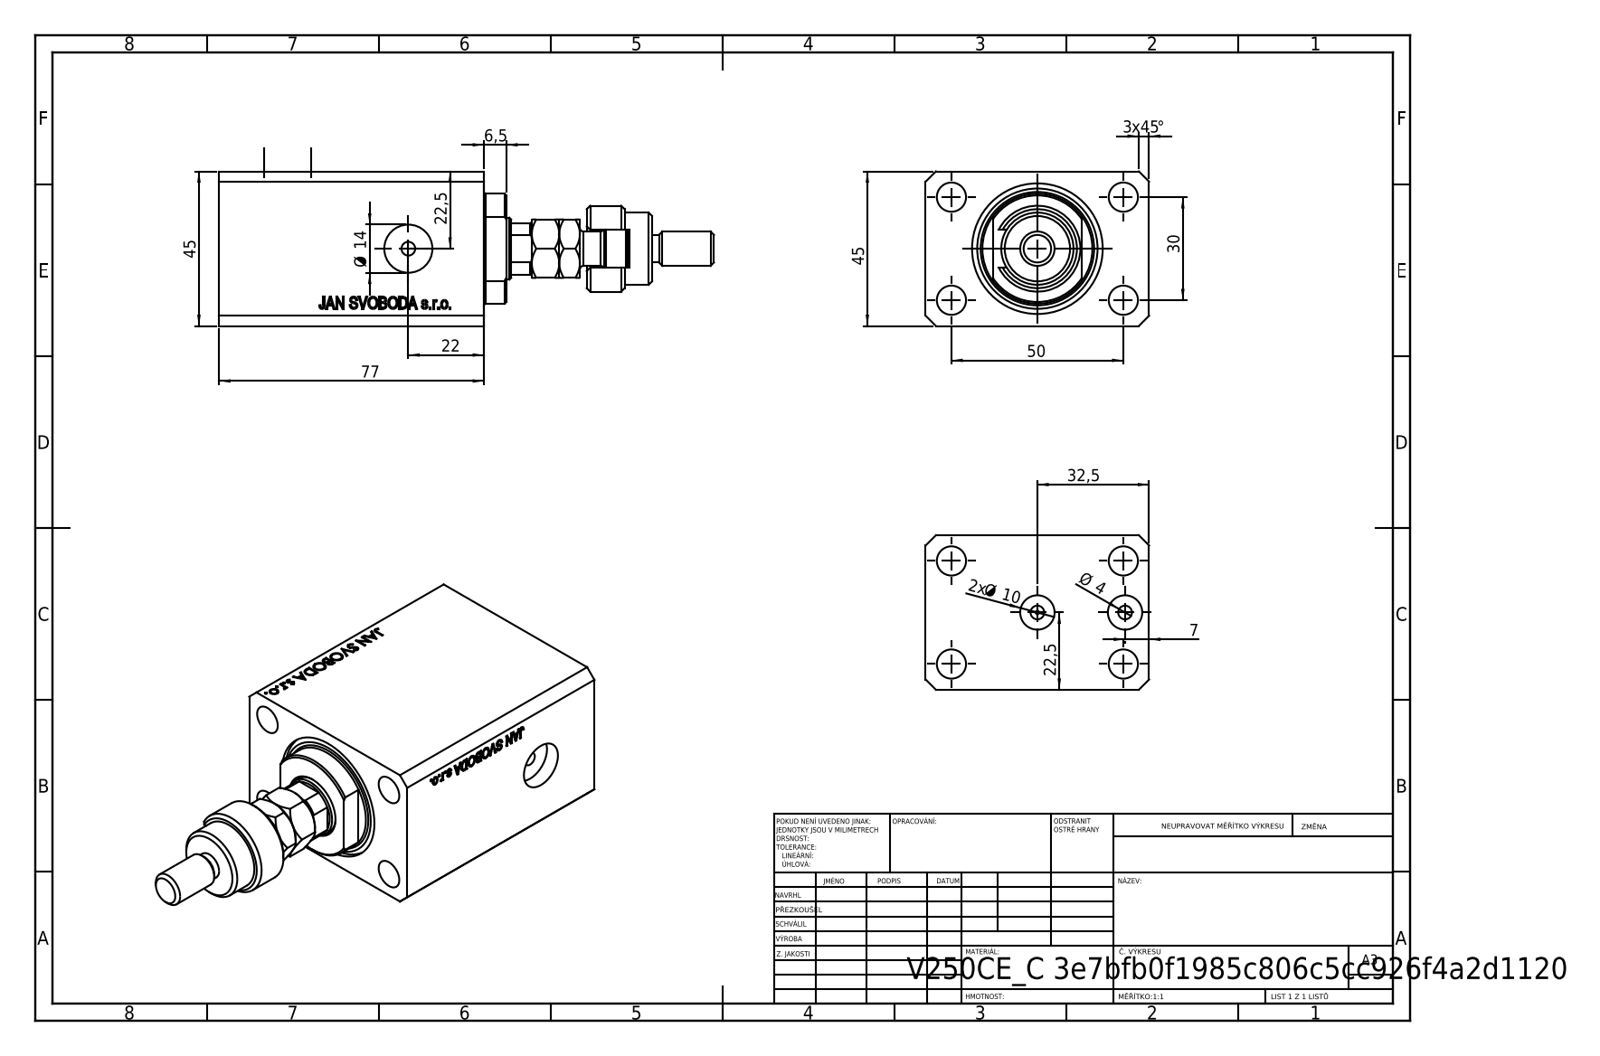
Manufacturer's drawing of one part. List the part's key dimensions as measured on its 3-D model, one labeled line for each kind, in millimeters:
Part name (STEP PRODUCT): V250CE_VC_C; MFA; V250CE_C_Body; FEMALE_PART_FOR_DFA (+1 more)
STEP written by: SolidWorks 2019 (CONFIG_CONTROL_DESIGN)
Units: millimetres
Bodies: 5 solids, 957 faces (456 planar, 63 cylindrical, 438 other)
Overall size (bounding box): 143.9 × 65 × 45
Volume: 215 291 mm³ · Surface area: 58 273 mm²
Round holes (diameter × count): ⌀8.5 ×5, ⌀4 ×4, ⌀14 ×2, ⌀1.25 ×1, ⌀10 ×1, ⌀18 ×1, ⌀38 ×1
Round bosses / shafts (diameter × count): ⌀25 ×1, ⌀21 ×1, ⌀16 ×1, ⌀10 ×1, ⌀8 ×1
Partial cylindrical surfaces — rounded edges, fillets, slot ends (radius × count): R5.5 ×1, R8.5 ×1, R8.75 ×1, R16 ×1
Main face-to-face distances: 45, 65, 77, 51.9, 25.1, 6.9, 70.1, 14, 6.5, 73.52
Hole centre spacings: 29.15, 15.01, 30, 50, 52.68, 58.31, 25.5, 33
